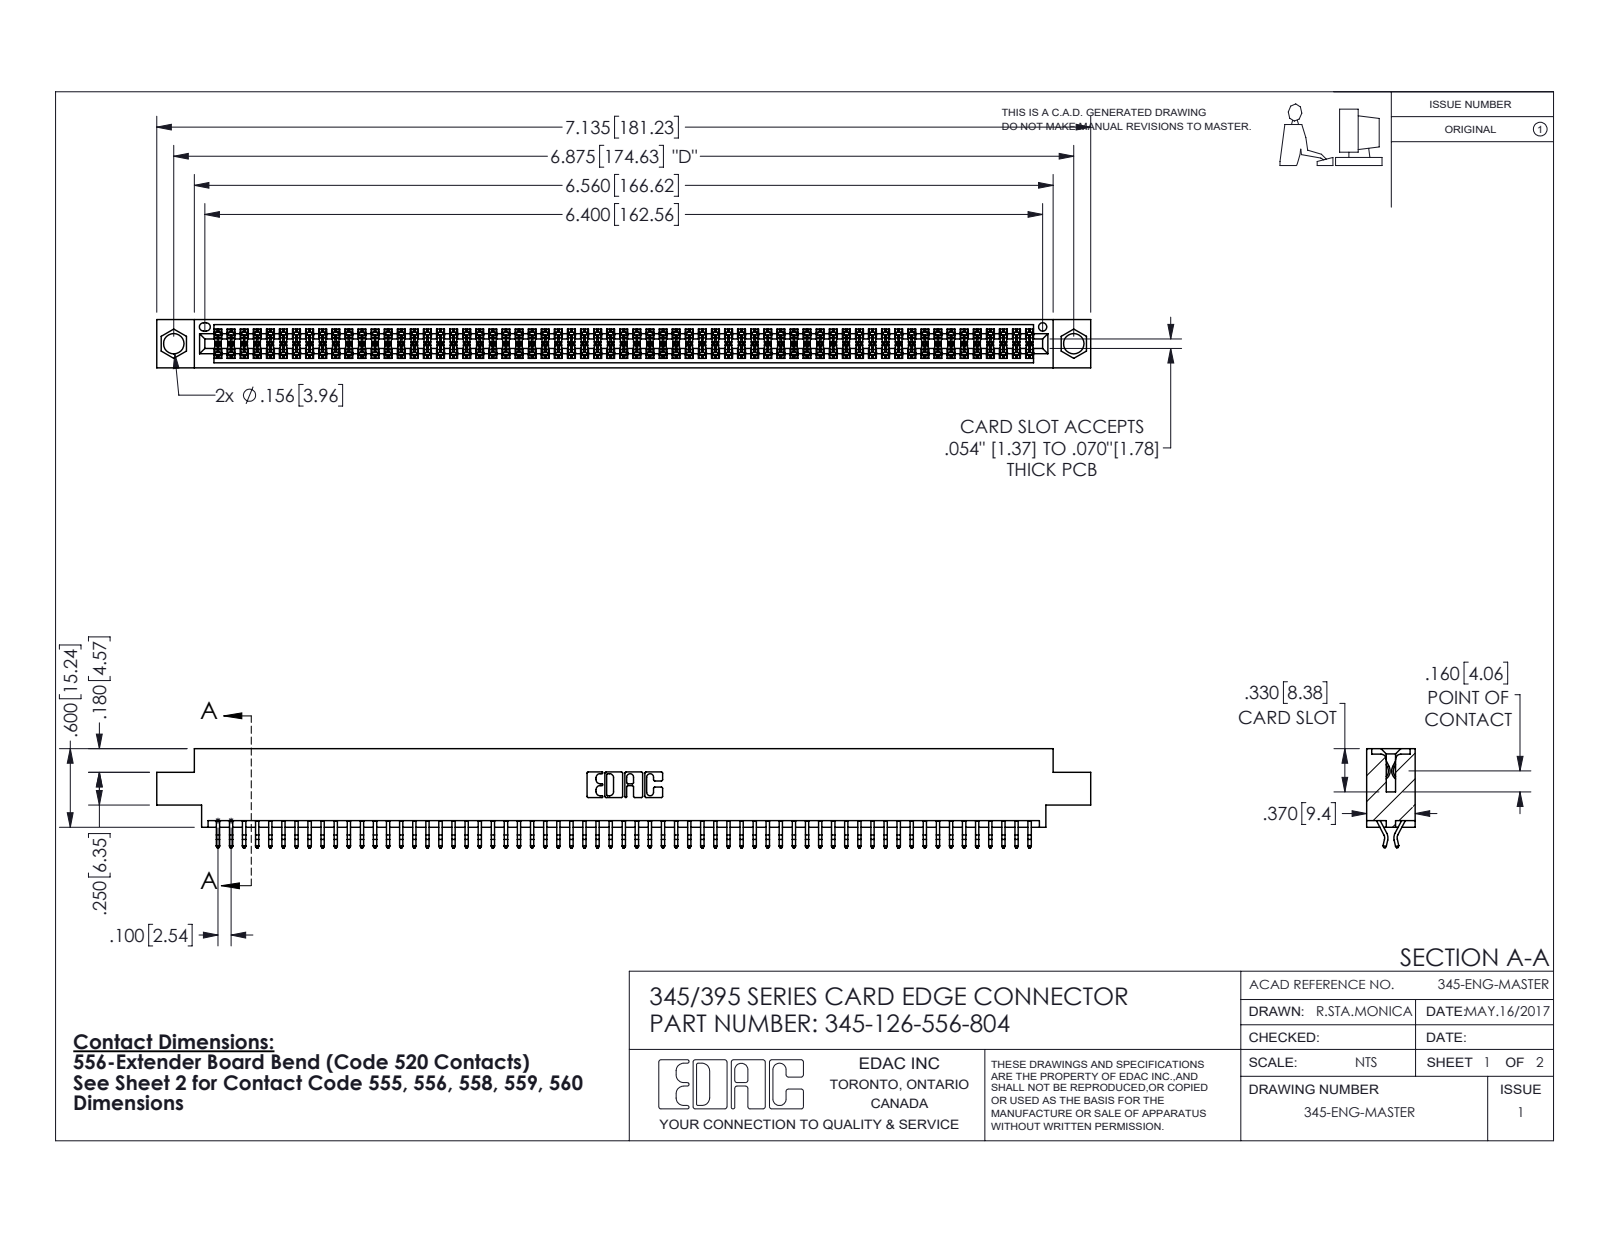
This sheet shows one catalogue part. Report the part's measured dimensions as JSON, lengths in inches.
{"part_name": "345-292-001_556 Tail; 345 Part_0.170 Offset - 0.156 Dia-TI; 345-126-556-804", "step_written_by": "SolidWorks 2020 (CONFIG_CONTROL_DESIGN)", "units": "inches", "bodies": {"solids": 127, "faces": 7200, "planar": 4760, "cylindrical": 2440, "other": 0}, "overall_size": [7.135, 0.757, 0.37], "volume_in3": 1.073, "surface_area_in2": 40.72, "round_holes": [[0.156, 2], [0.064, 1]], "partial_cylinders_radius": [[0.006, 252], [0.01, 22], [0.007, 6], [0.031, 6], [0.026, 3], [0.01, 2], [0.014, 2], [0.019, 2]], "face_to_face_distances": [0.072, 0.298, 0.37, 0.2, 0.025, 0.098, 0.272, 0.225, 0.175, 0.149], "hole_center_spacings": [0.27, 6.639, 6.875]}
